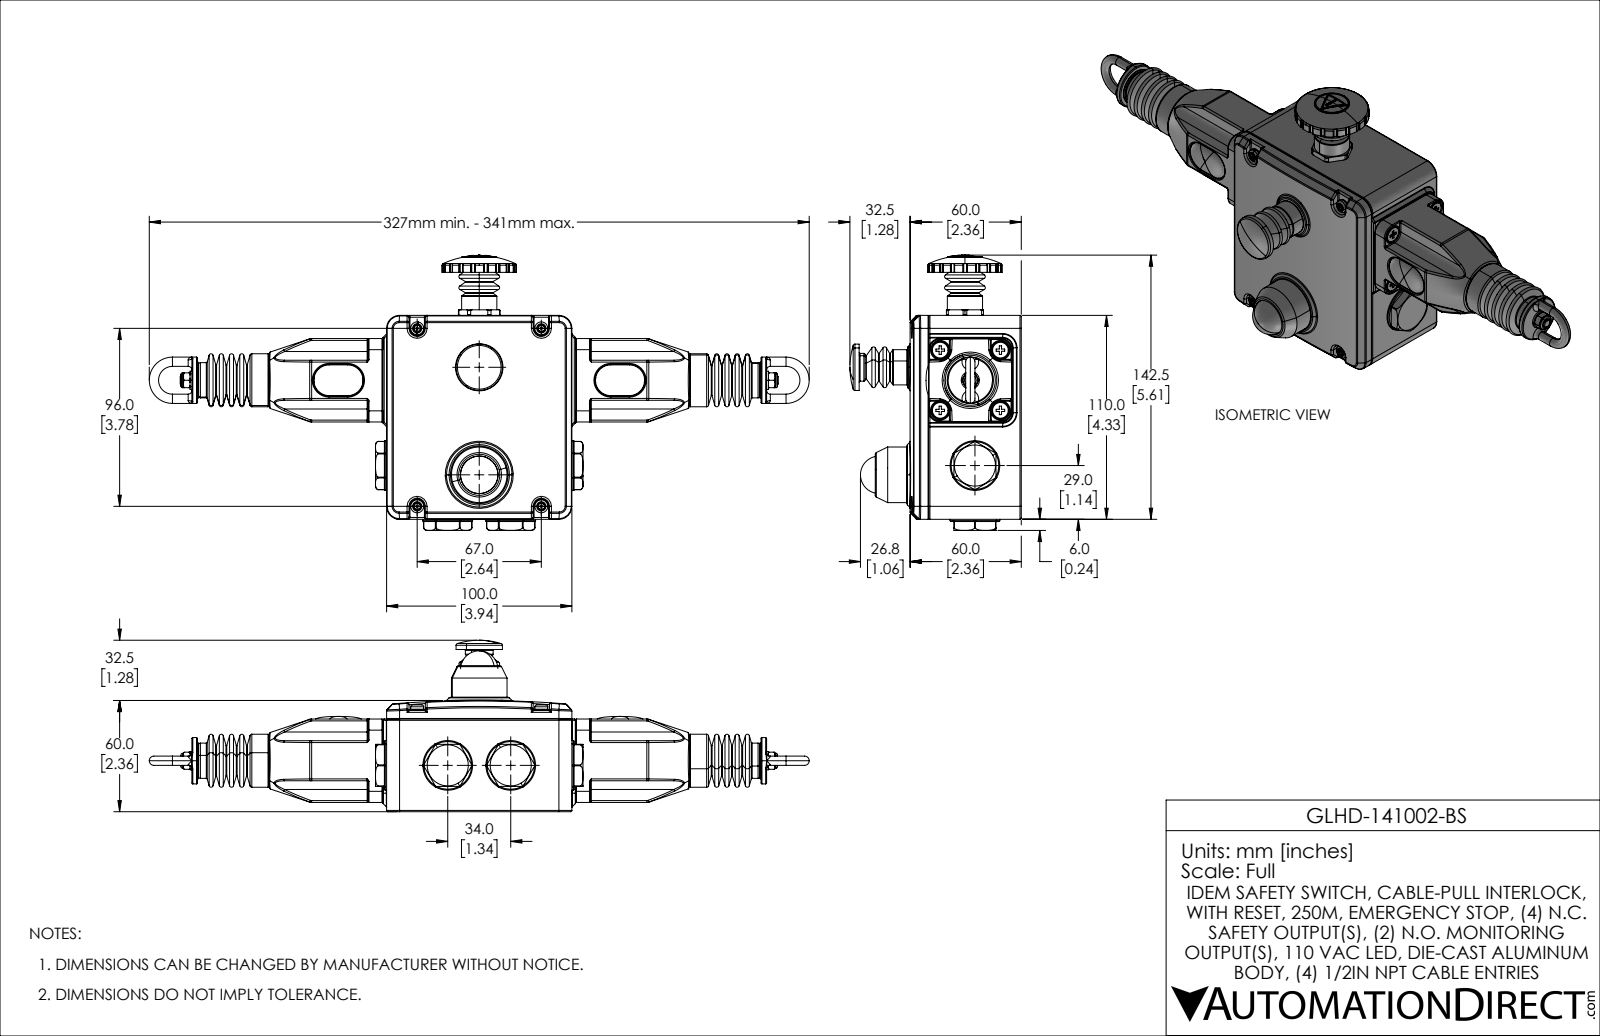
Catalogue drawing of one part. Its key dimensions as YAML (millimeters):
part_name: "GLHD-141002-AS"
step_written_by: "SolidWorks 2021 (AUTOMOTIVE_DESIGN)"
units: millimeters
bodies: {solids: 47, faces: 5551, planar: 1509, cylindrical: 1887, other: 2155}
overall_size: [356.2, 148.5, 92.5]
volume: 357200
surface_area: 228300
round_holes:
  - {diameter: 5, count: 11}
  - {diameter: 5.3, count: 5}
  - {diameter: 2.4, count: 4}
  - {diameter: 3.3, count: 4}
  - {diameter: 4, count: 4}
  - {diameter: 4.8, count: 4}
  - {diameter: 5.4, count: 4}
  - {diameter: 5.8, count: 4}
  - {diameter: 9, count: 4}
  - {diameter: 9.5, count: 4}
  - {diameter: 1.7, count: 3}
  - {diameter: 2.6, count: 3}
round_bosses_or_shafts:
  - {diameter: 6, count: 7}
  - {diameter: 7, count: 5}
  - {diameter: 8.5, count: 4}
  - {diameter: 4.4, count: 4}
  - {diameter: 3.5, count: 4}
  - {diameter: 1.3, count: 4}
  - {diameter: 26.8, count: 3}
  - {diameter: 19.4, count: 3}
partial_cylinders:
  - {radius: 0.5, count: 287}
  - {radius: 0.2, count: 148}
  - {radius: 1, count: 142}
  - {radius: 0.7, count: 80}
  - {radius: 0.3, count: 32}
  - {radius: 0.1, count: 17}
  - {radius: 0.2, count: 14}
  - {radius: 2, count: 14}
face_to_face_distances: [3.5, 54.8, 2.9, 51.9, 110, 45, 98.5, 4, 2, 11.7]
hole_center_spacings: [5.8, 9.5, 23, 32.5, 48, 48.6, 76.5, 88.6]
